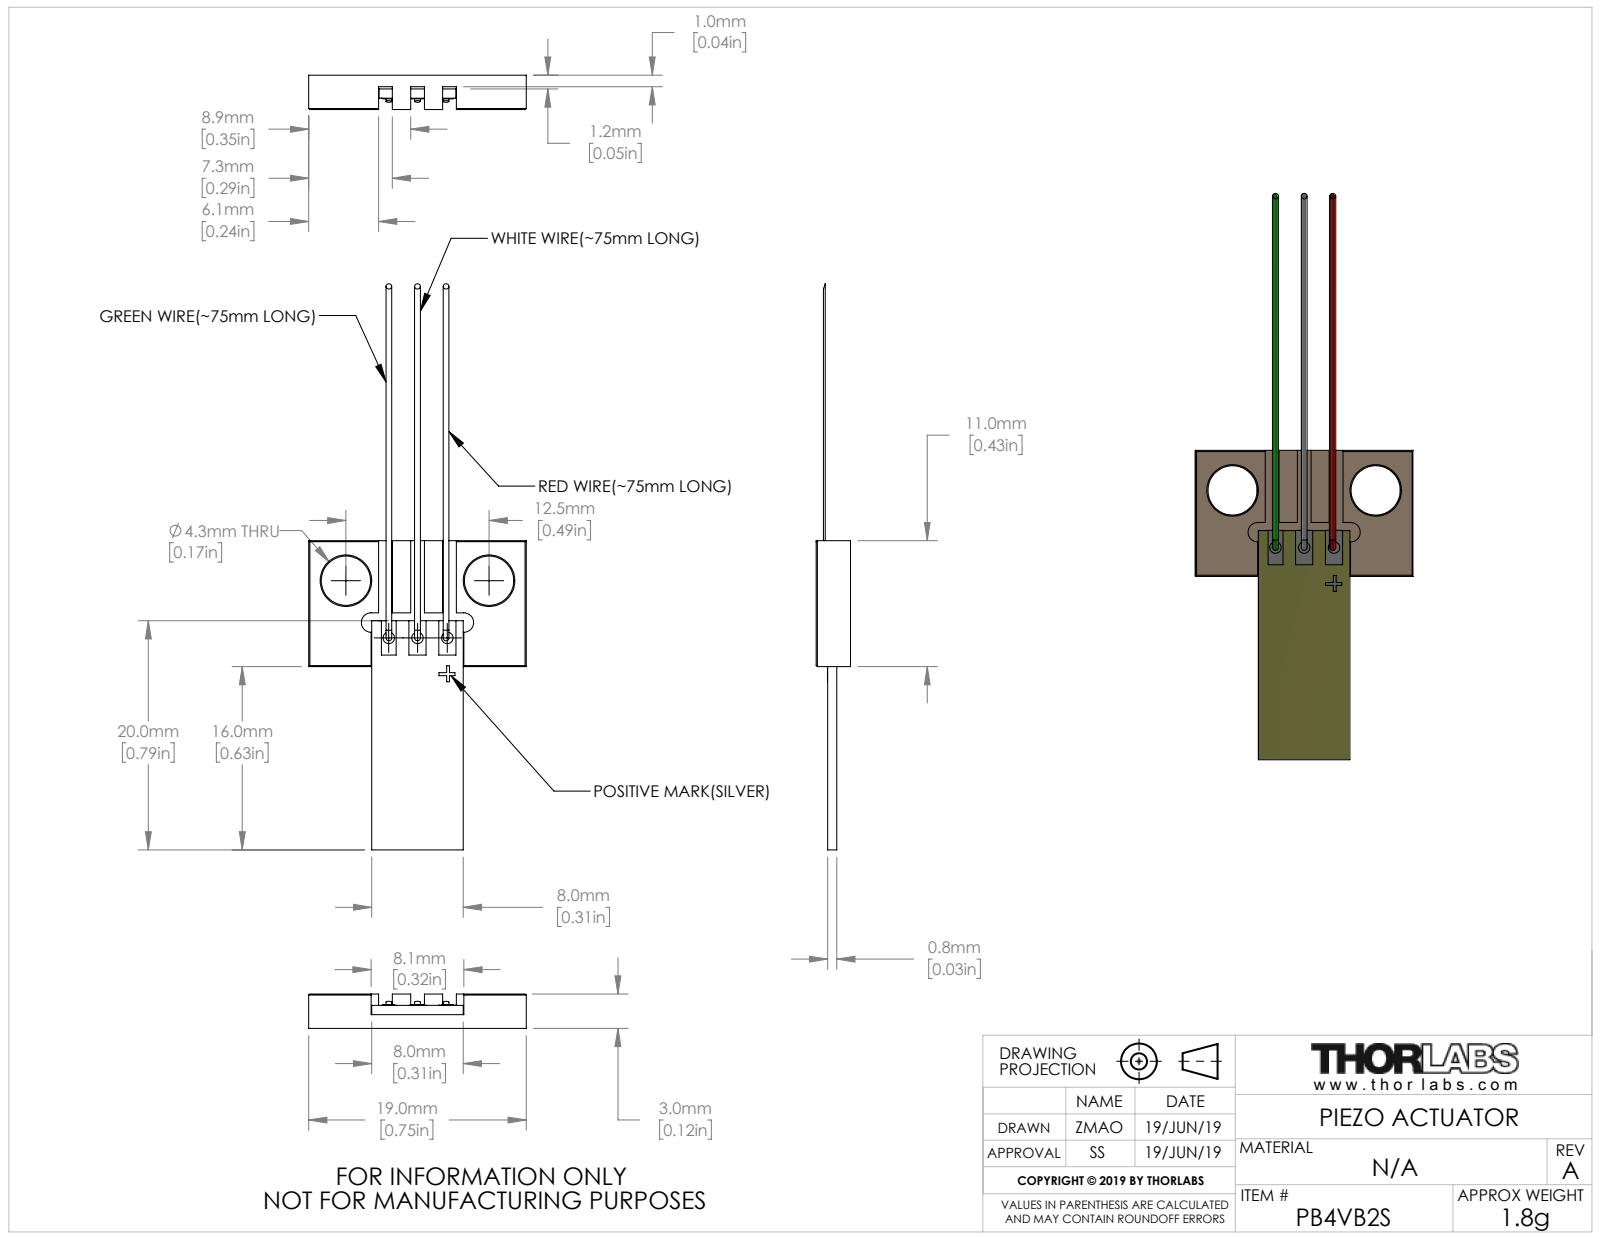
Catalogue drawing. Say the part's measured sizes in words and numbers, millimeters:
The part is named "CTN014140". Its 3-D file was written by "SolidWorks 2018 (AUTOMOTIVE_DESIGN)". It is 2 solids with 103 faces: 74 planar, 13 cylindrical and 16 other. Overall it measures 49.42 by 19 by 3 millimeters. Its volume is 552 cubic millimeters and its surface area 1 169 square millimeters. Round holes: 2 of diameter 4.3. Round bosses or shafts: 3 of diameter 1. Partial cylindrical surfaces (rounded edges, fillets, slot ends): 2 of radius 0.85. The main face-to-face distances are 1.2, 1, 2, 0.8, 1.8, 3, 2.8, 11, 19, 5.5. The hole center spacings are 12.5.
